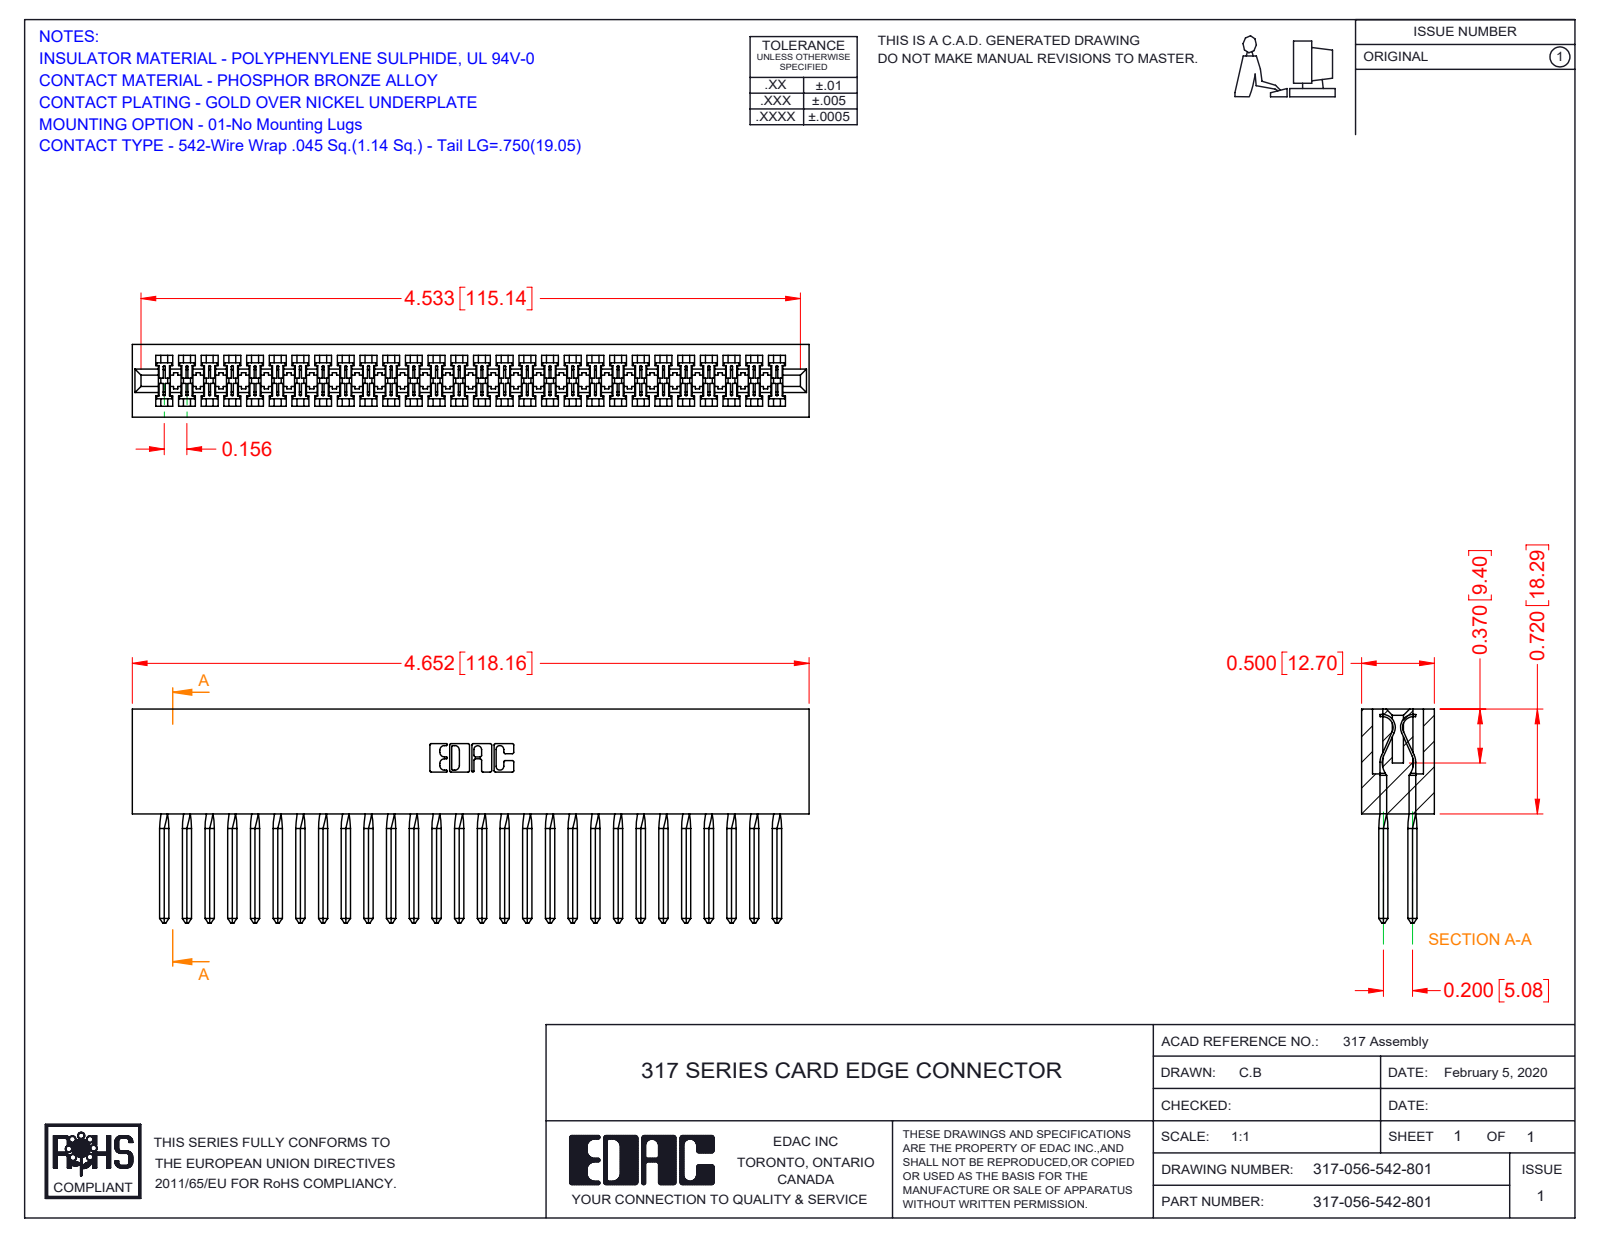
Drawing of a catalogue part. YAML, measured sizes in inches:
part_name: "317-056-542-801; 317-290-003_542; 317 Part_Lugless"
step_written_by: "SolidWorks 2016 (CONFIG_CONTROL_DESIGN)"
units: inches
bodies: {solids: 57, faces: 3282, planar: 2626, cylindrical: 432, other: 224}
overall_size: [4.652, 1.47, 0.5]
volume: 1.259
surface_area: 44.06
partial_cylinders:
  - {radius: 0.006, count: 112}
  - {radius: 0.01, count: 22}
  - {radius: 0.007, count: 6}
  - {radius: 0.031, count: 6}
  - {radius: 0.026, count: 3}
  - {radius: 0.074, count: 2}
  - {radius: 0.089, count: 2}
  - {radius: 0.1, count: 2}
face_to_face_distances: [0.5, 0.075, 0.425, 0.35, 0.2, 0.116, 0.11, 0.046, 0.128, 0.372]
